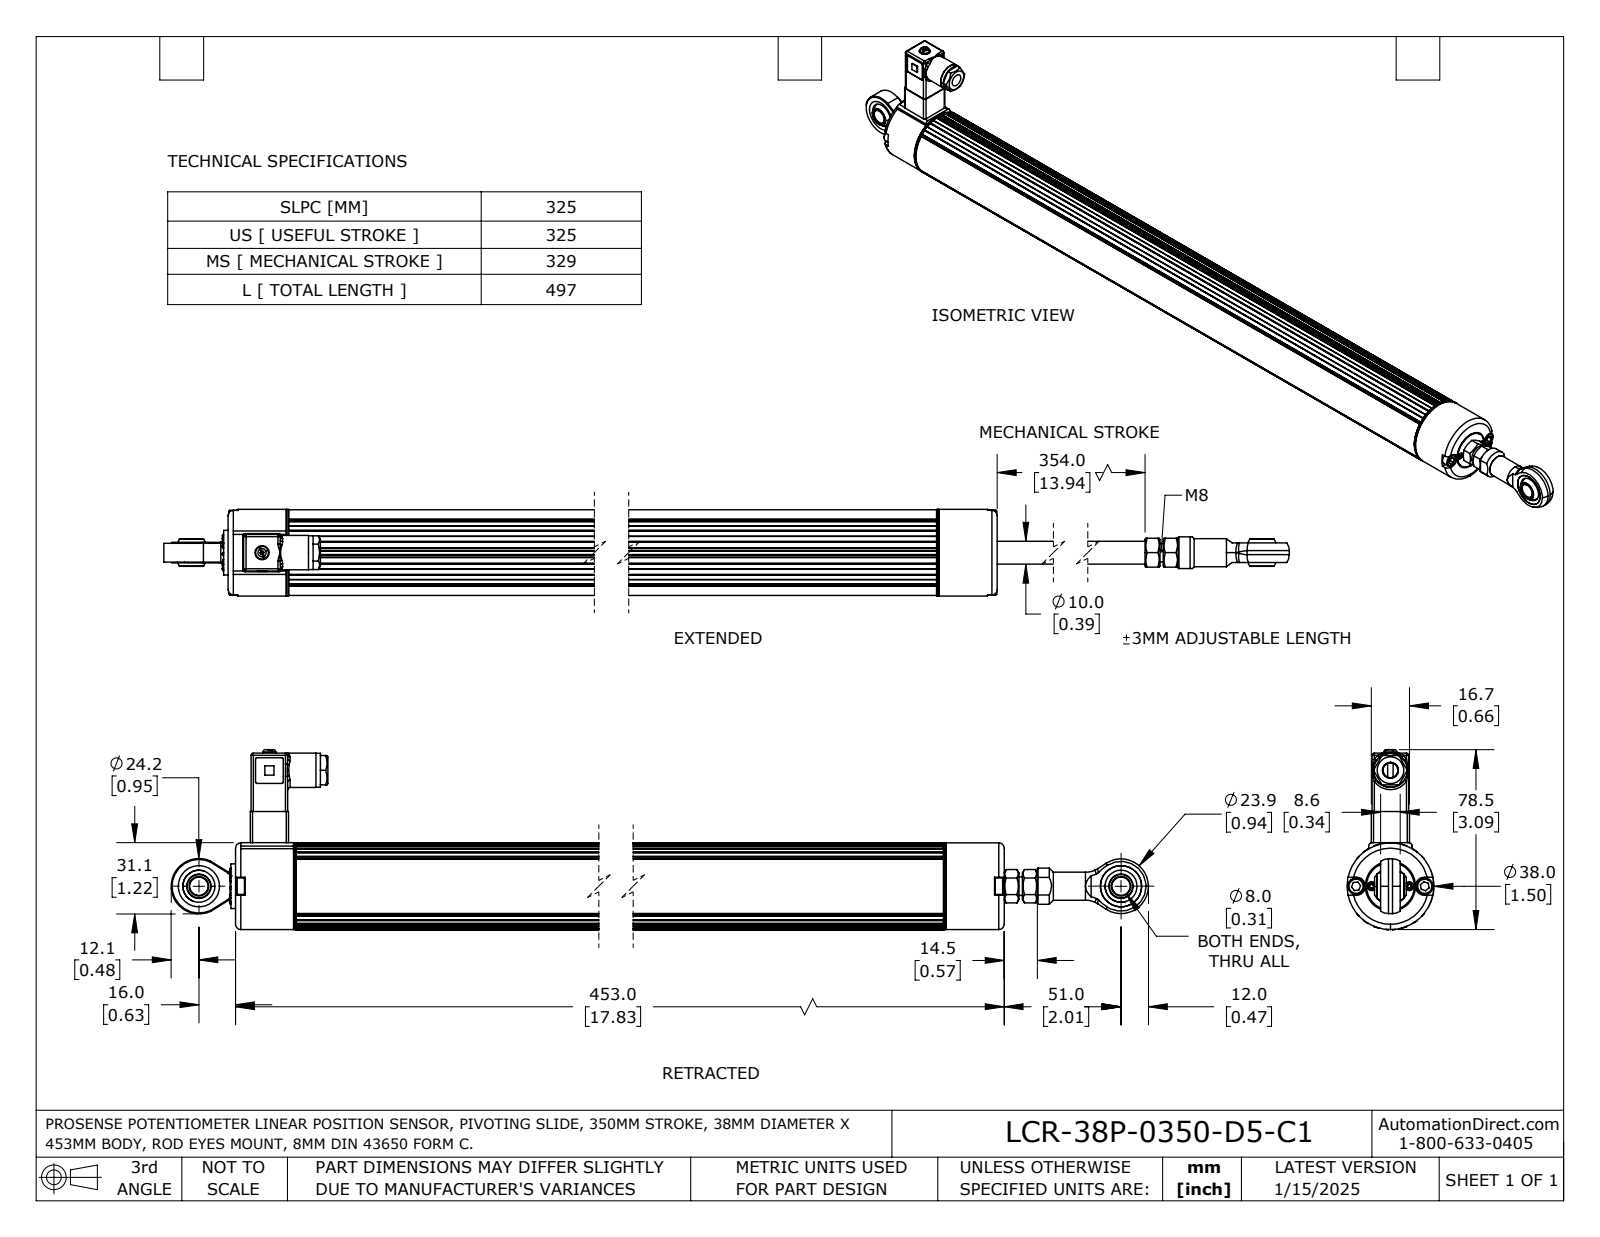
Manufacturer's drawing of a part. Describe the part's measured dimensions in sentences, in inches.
The part is named "LCR-38P-0350-D5-C1". Its 3-D file was written by "SolidWorks 2023 (AUTOMOTIVE_DESIGN)". It is 11 solids with 657 faces: 295 planar, 210 cylindrical and 152 other. Overall it measures 21.419 by 3.093 by 1.488 inches. Its volume is 31.62 cubic inches and its surface area 142.6 square inches. Round holes: 6 of diameter 0.102, 4 of diameter 0.091, 3 of diameter 0.315, 3 of diameter 0.551, 2 of diameter 0.094, 2 of diameter 0.1, 2 of diameter 0.111, 2 of diameter 0.134, 2 of diameter 0.152, 2 of diameter 0.165, 1 of diameter 0.079, 1 of diameter 0.118. Round bosses or shafts: 6 of diameter 0.063, 4 of diameter 0.283, 4 of diameter 0.15, 2 of diameter 0.48, 2 of diameter 0.079, 1 of diameter 1.488, 1 of diameter 0.823, 1 of diameter 0.768. Partial cylindrical surfaces (rounded edges, fillets, slot ends): 32 of radius 0.008, 20 of radius 0.039, 12 of radius 0.02, 6 of radius 0.016, 2 of radius 0.012, 2 of radius 0.059, 2 of radius 0.083, 2 of radius 0.098. The main face-to-face distances are 15.748, 1.043, 16.791, 0.031, 0.045, 0.612, 0.598, 0.014, 0.644, 0.138. The hole center spacings are 0.632, 0.075, 0.634, 0.264, 0.268, 0.285, 0.323, 0.394.
